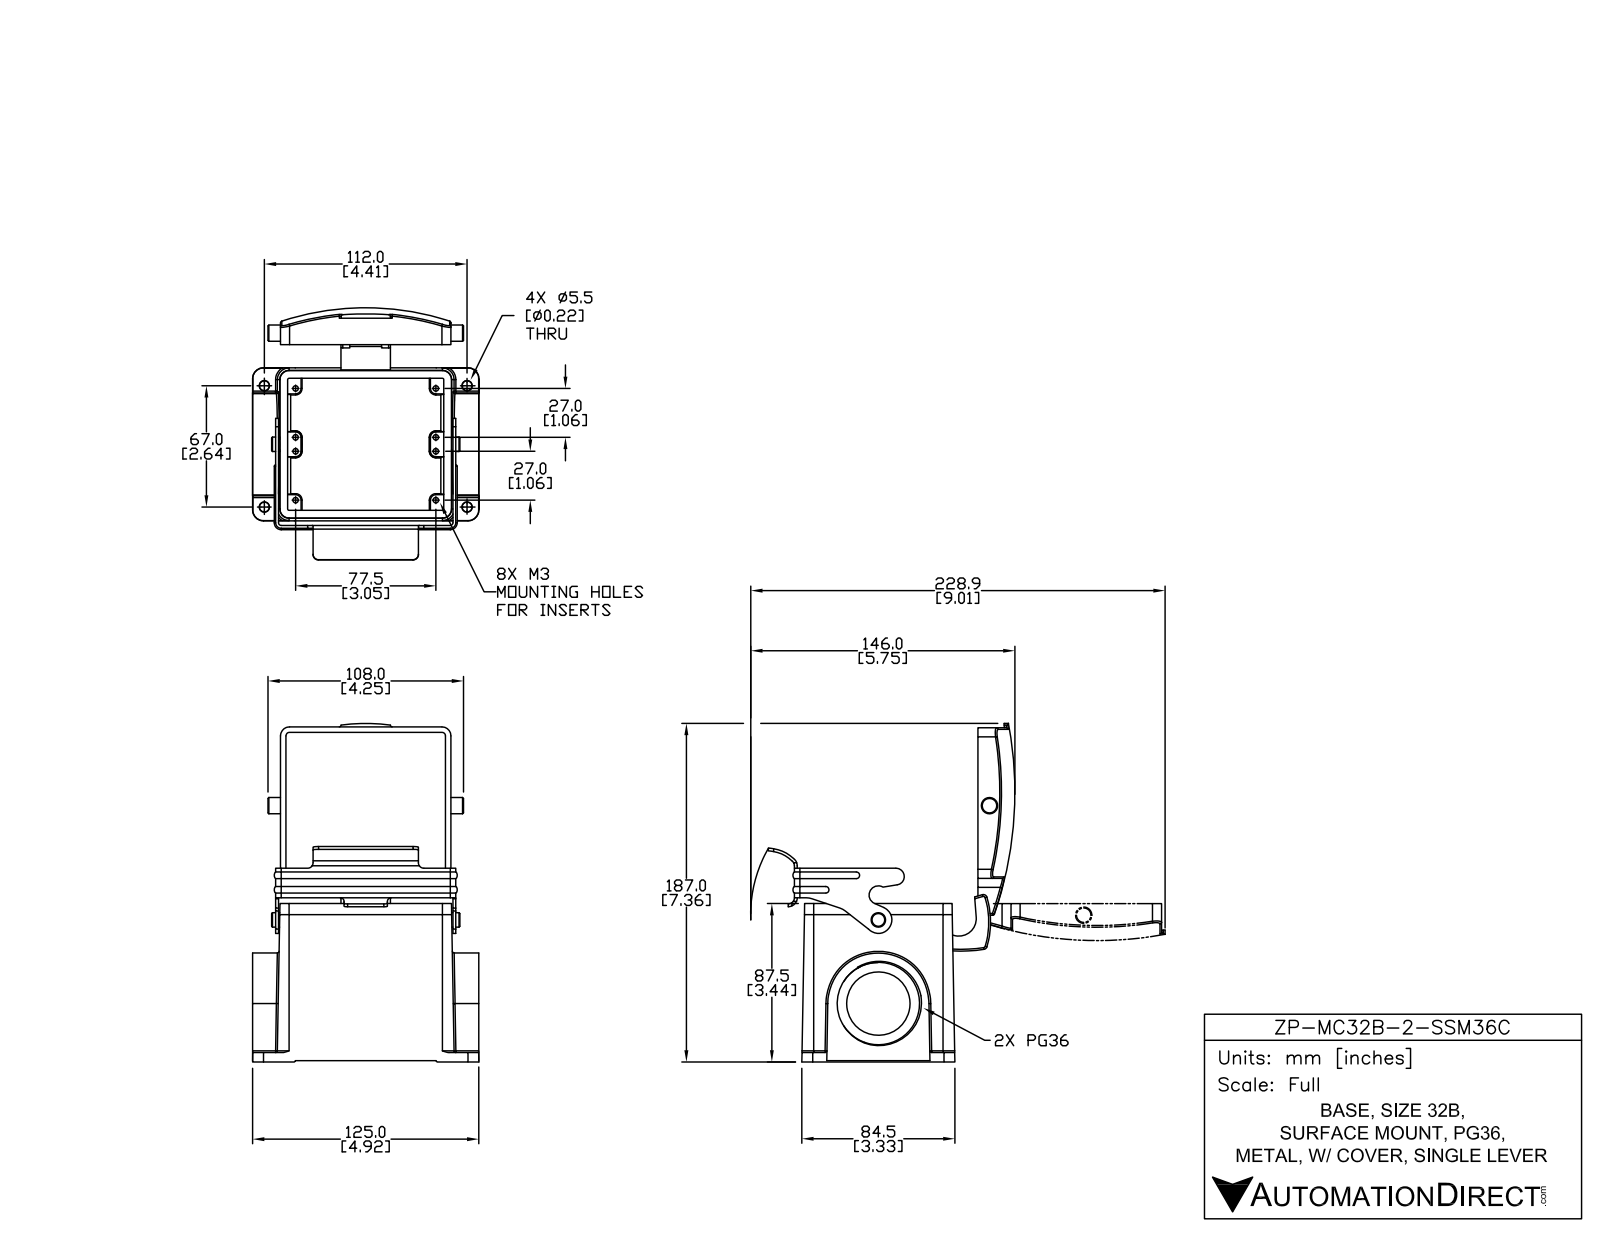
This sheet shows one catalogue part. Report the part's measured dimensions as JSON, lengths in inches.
{"part_name": "ZP-MC32B-2-SSM36C", "step_written_by": "SolidWorks 2014 (AUTOMOTIVE_DESIGN)", "units": "inches", "bodies": {"solids": 2, "faces": 440, "planar": 162, "cylindrical": 176, "other": 102}, "overall_size": [7.381, 5.484, 4.895], "volume_in3": 18.59, "surface_area_in2": 198.6, "round_holes": [[0.118, 9], [1.378, 1], [1.791, 1]], "round_bosses_or_shafts": [[0.354, 1], [0.315, 1]], "partial_cylinders_radius": [[0.039, 15], [0.079, 10], [0.197, 6], [0.03, 4], [0.118, 4], [0.059, 2], [0.12, 2], [0.315, 2]], "face_to_face_distances": [2.872, 0.305, 0.03, 0.335, 0.118, 0.061, 0.827, 4.067, 0.549, 4.344], "hole_center_spacings": [1.063, 1.366, 3.051, 3.231, 3.343, 0.303, 2.429, 3.066]}
